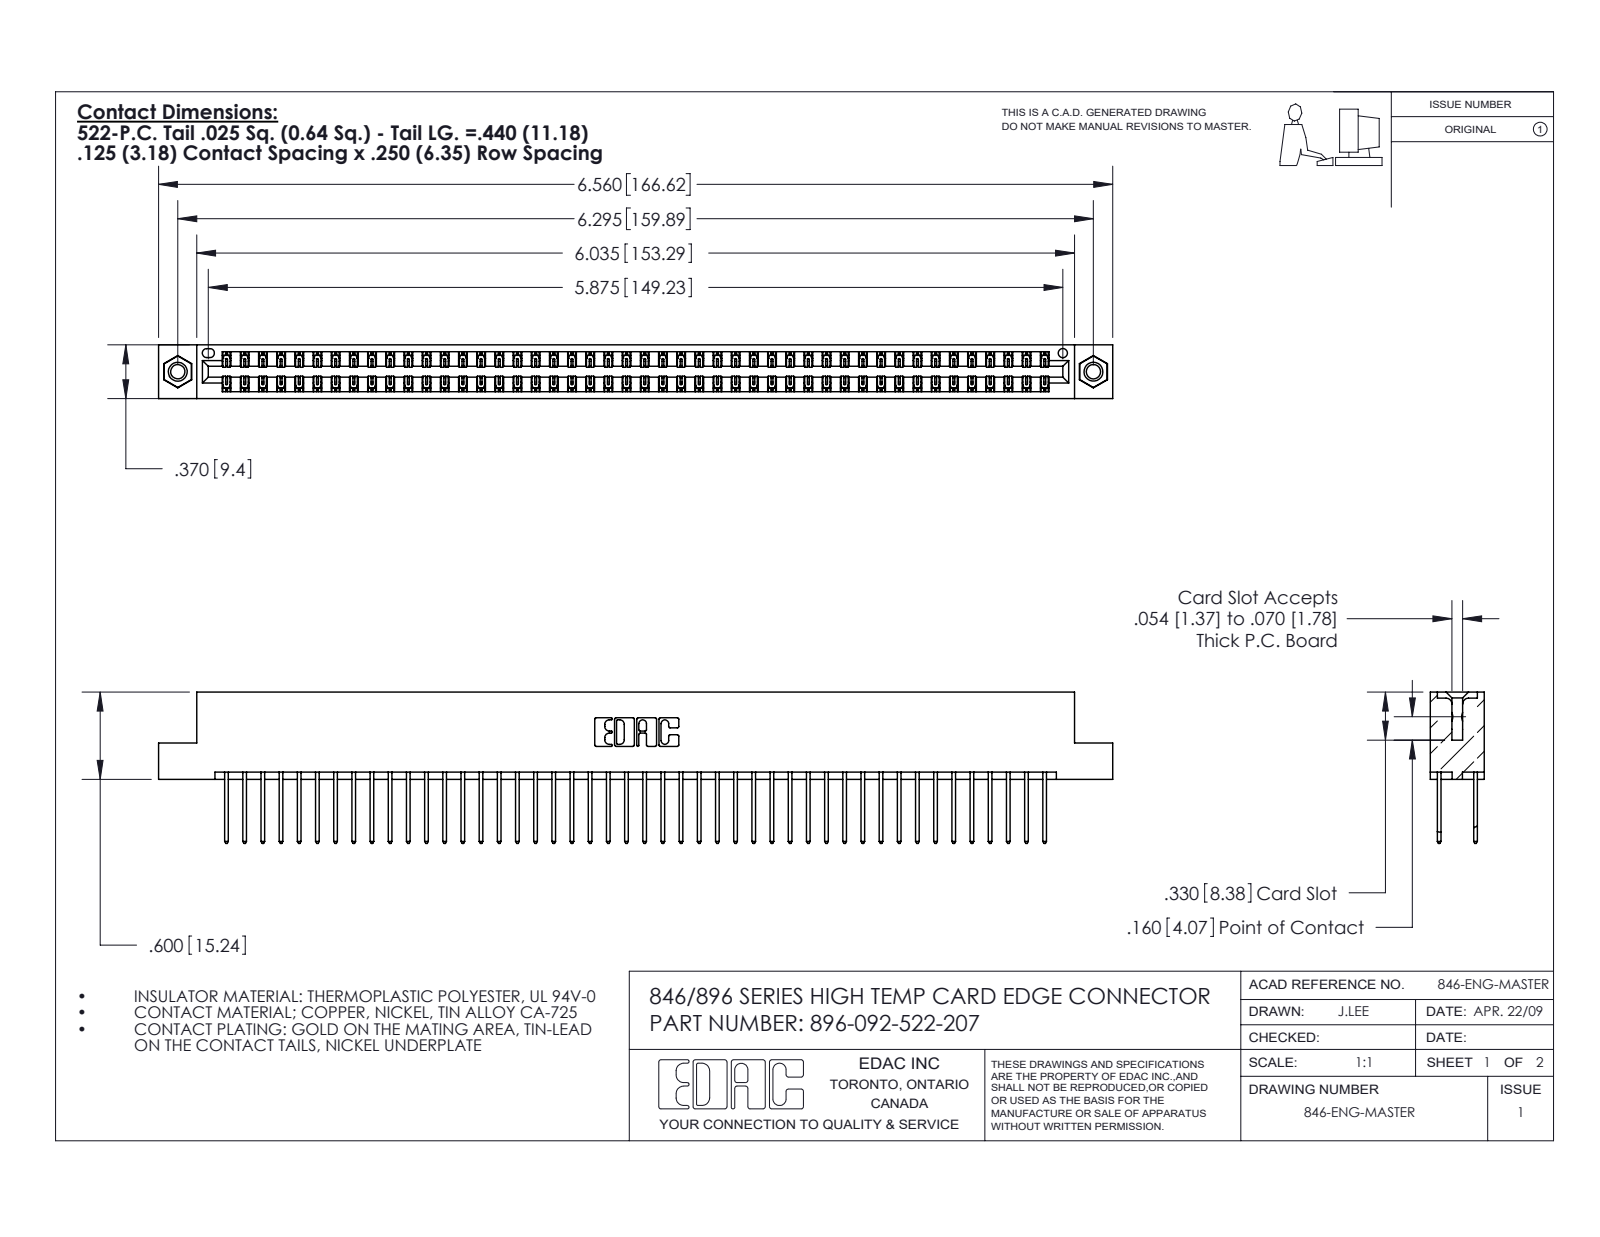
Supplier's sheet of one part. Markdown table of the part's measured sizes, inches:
| quantity | value |
| --- | --- |
| part name | 346 Part_Flush Mounting Lugs - 0.156 Dia-TI; 345-250-001_345-250-005-103; 345-292-001_345-293-122; 396-092-522-207 |
| STEP written by | SolidWorks 2016 (CONFIG_CONTROL_DESIGN) |
| units | inches |
| bodies | 95 solids, 4966 faces (3328 planar, 1622 cylindrical, 16 other) |
| overall size | 6.56 × 1.04 × 0.37 |
| volume | 1.007 in³ |
| surface area | 37 in² |
| round holes (diameter × count) | 0.098 × 2, 0.125 × 2, 0.156 × 2, 0.064 × 1 |
| round bosses / shafts (diameter × count) | 0.155 × 2 |
| partial cylindrical surfaces (radius × count) | 0.006 × 138, 0.01 × 92, 0.01 × 22, 0.007 × 6, 0.031 × 6, 0.026 × 3, 0.014 × 2, 0.022 × 2 |
| main face-to-face distances | 0.048, 0.322, 0.25, 0.37, 0.072, 0.298, 0.025, 0.275, 0.148, 0.222 |
| hole center spacings | 0.246, 6.086, 6.295 |
